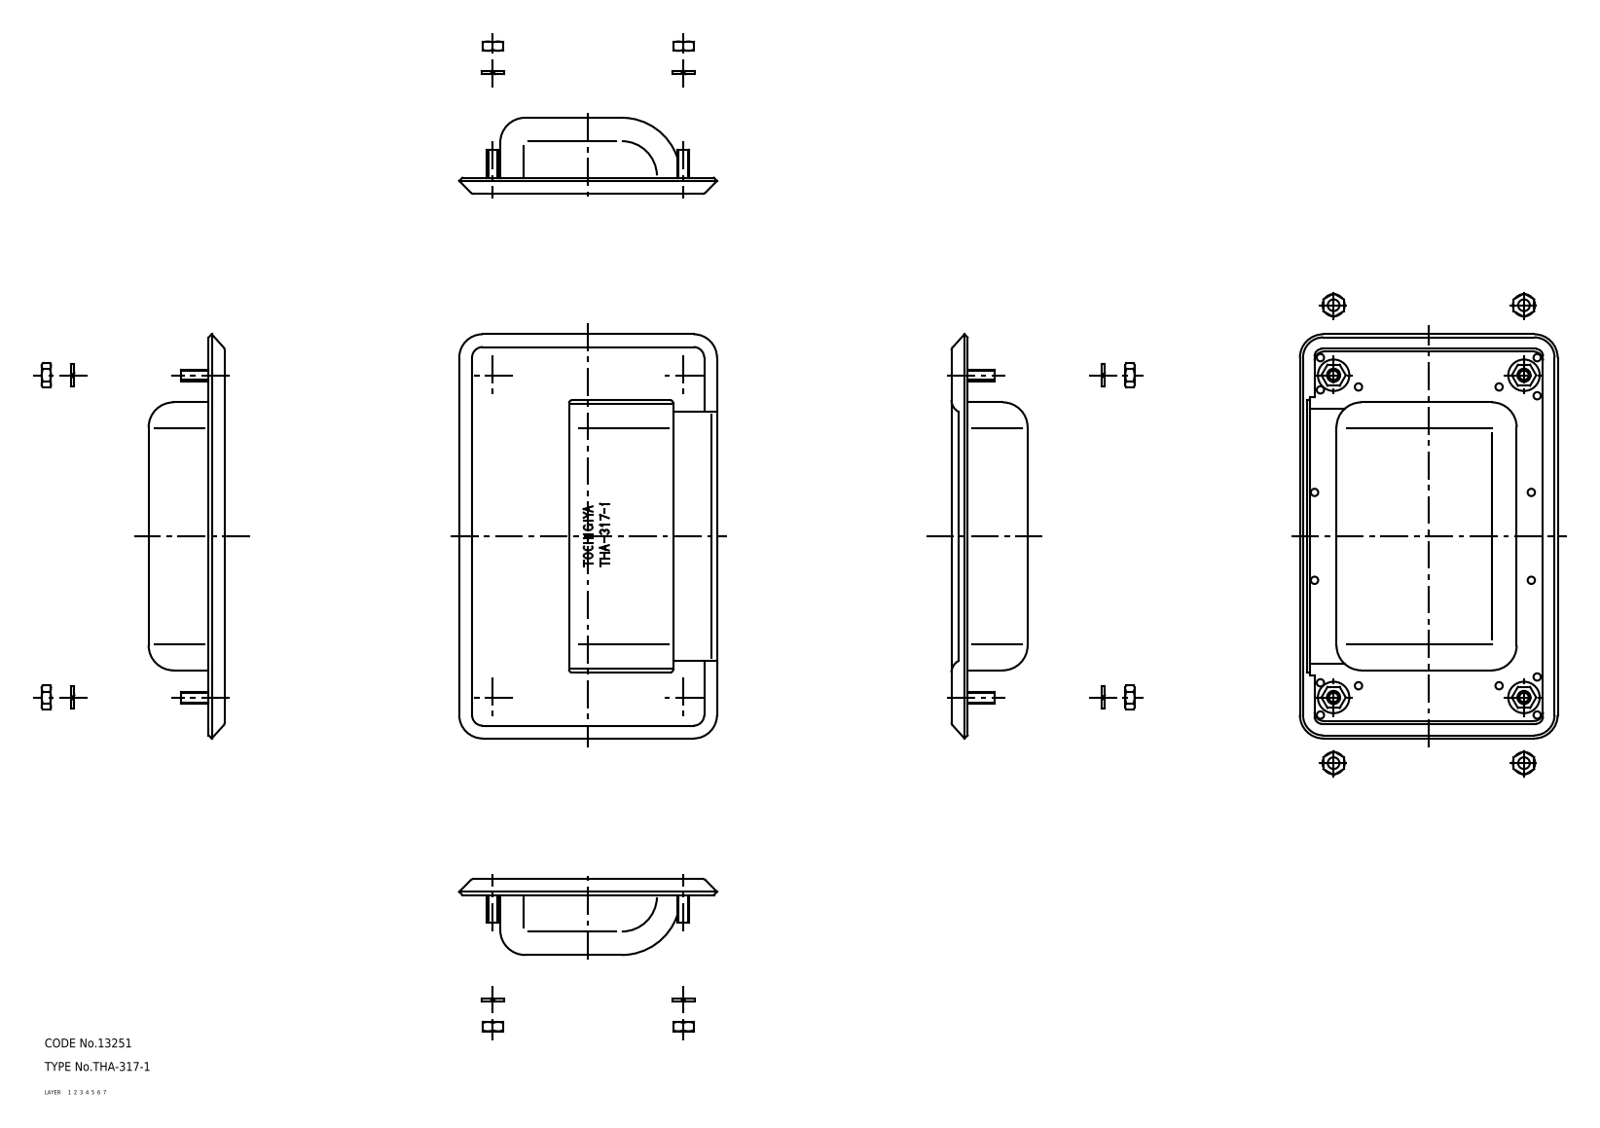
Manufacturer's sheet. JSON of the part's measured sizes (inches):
{"part_name": "washer; bolt; nut; cover (+2 more)", "step_written_by": "CADfix (AUTOMOTIVE_DESIGN)", "units": "inches", "bodies": {"solids": 14, "faces": 499, "planar": 0, "cylindrical": 0, "other": 499}, "overall_size": [5.433, 3.465, 1.024], "volume_in3": 1.233, "surface_area_in2": 85.53}
